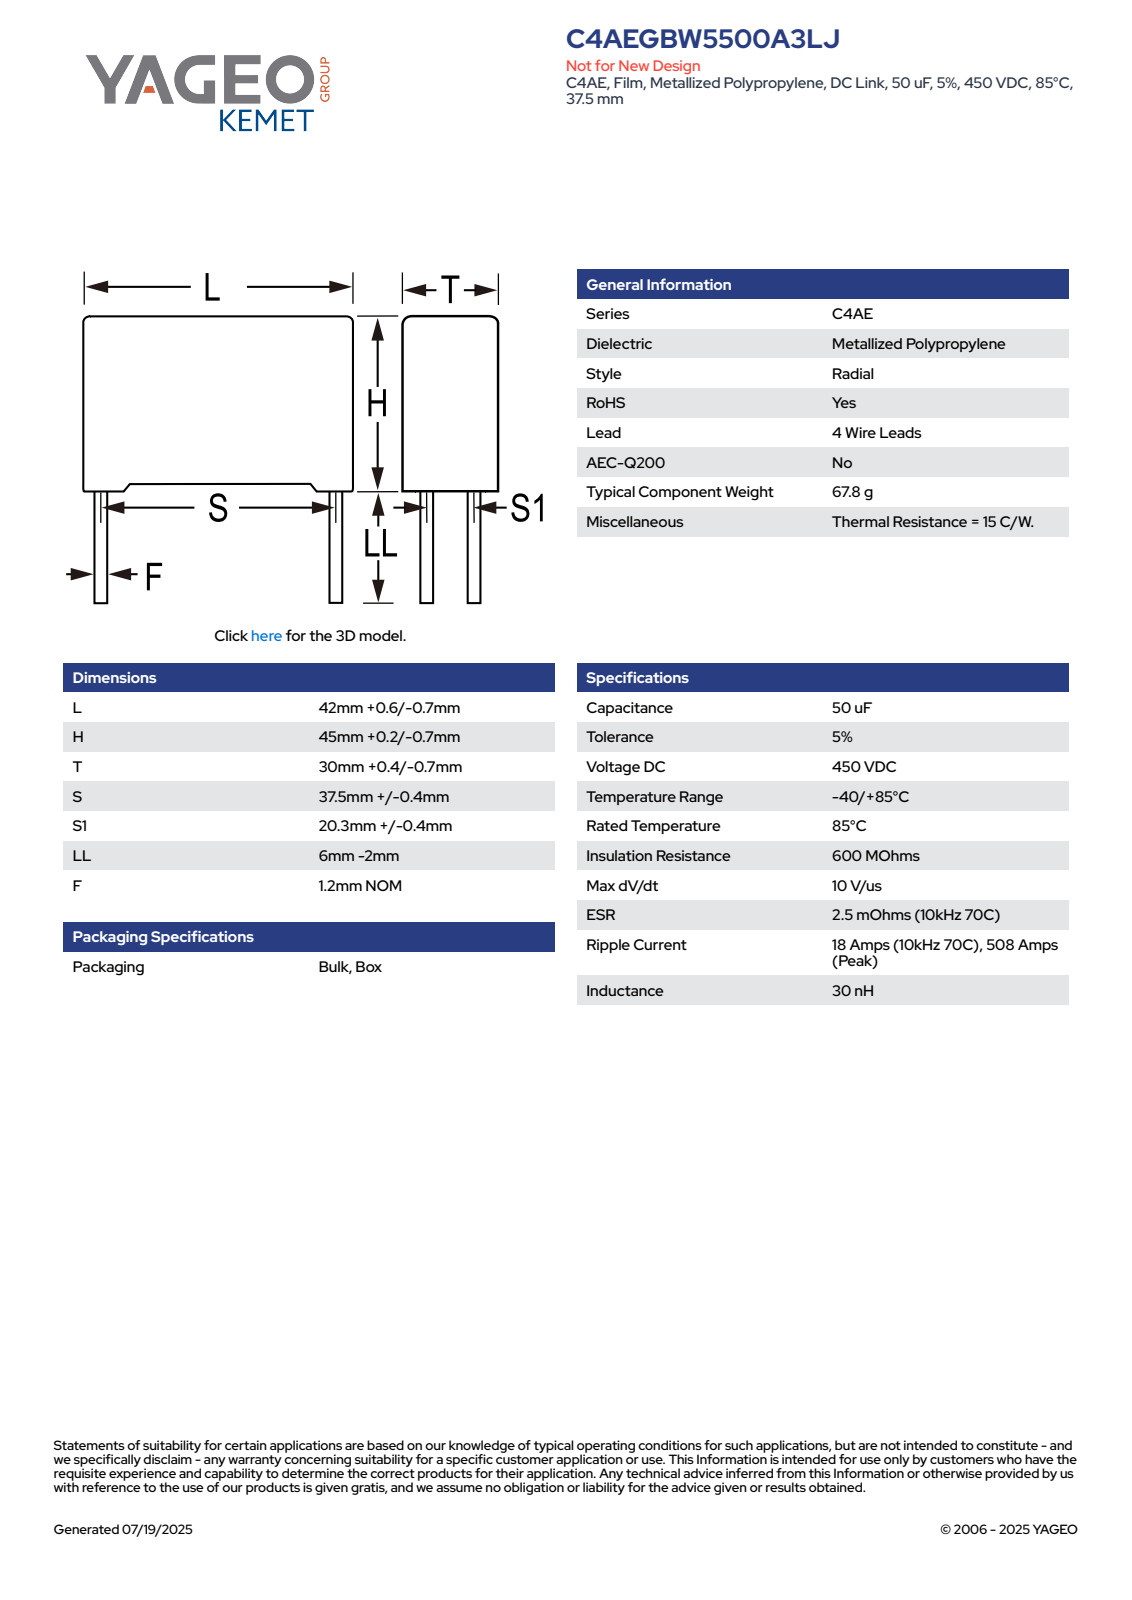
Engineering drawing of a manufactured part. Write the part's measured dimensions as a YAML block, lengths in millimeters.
part_name: "CFP_RB4_42X45X30_L42.6H45.2T30.4S37.5S120.3LL4F1.2"
step_written_by: "SolidWorks 2014 (AUTOMOTIVE_DESIGN)"
units: millimeters
bodies: {solids: 4, faces: 87, planar: 79, cylindrical: 8, other: 0}
overall_size: [49.2, 42.6, 30.41]
volume: 57045
surface_area: 9419
round_bosses_or_shafts:
  - {diameter: 1.2, count: 4}
face_to_face_distances: [30.4, 42.6, 43.87, 1.33, 45.2, 1.87, 40.73, 30.41, 38.86, 28.53]
